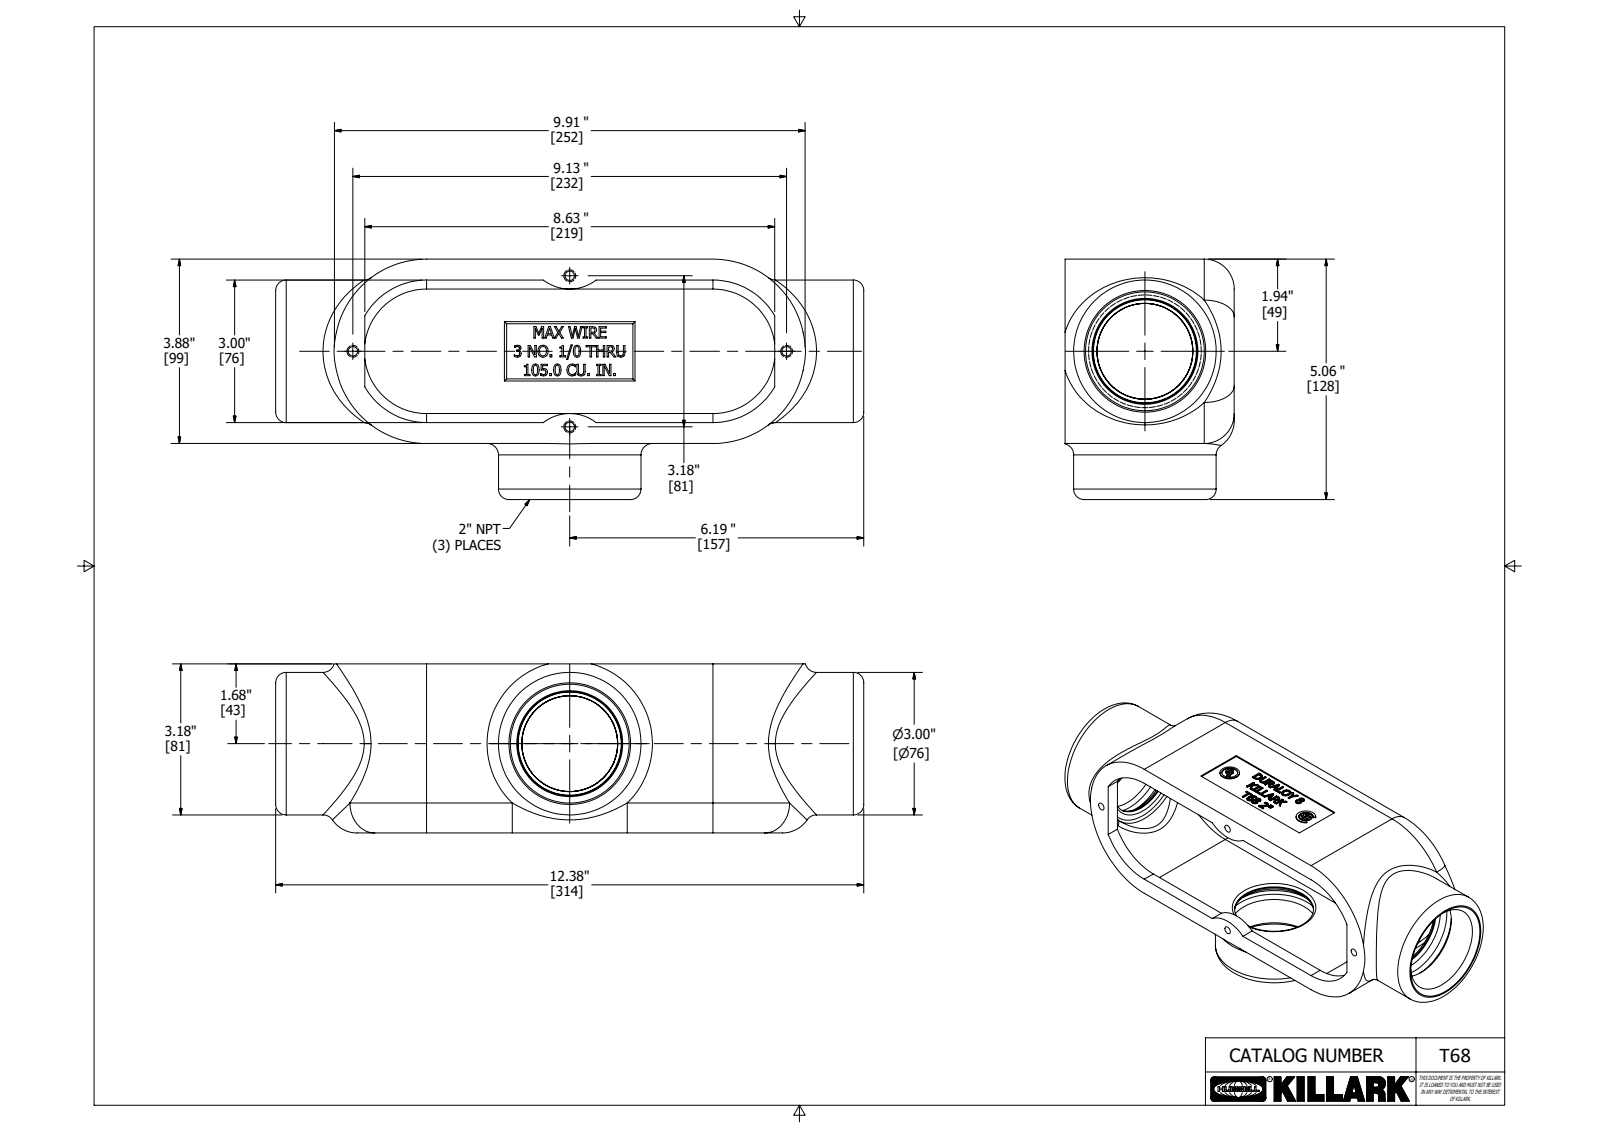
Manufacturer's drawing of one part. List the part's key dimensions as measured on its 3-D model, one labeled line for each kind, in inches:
Part name (STEP PRODUCT): 21745-2
STEP written by: Autodesk Inventor 2018 (AUTOMOTIVE_DESIGN)
Units: inches
Bodies: 1 solid, 830 faces (493 planar, 45 cylindrical, 292 other)
Overall size (bounding box): 12.381 × 5.059 × 3.62
Volume: 35.54 in³ · Surface area: 282.9 in²
Round holes (diameter × count): ⌀0.196 ×4, ⌀2.381 ×2, ⌀0.407 ×1
Round bosses / shafts (diameter × count): ⌀3 ×2, ⌀0.5 ×1
Partial cylindrical surfaces — rounded edges, fillets, slot ends (radius × count): R0.41 ×2, R0.63 ×2, R0.906 ×2, R1.5 ×2, R1.72 ×2, R1.94 ×2, R0.016 ×1, R0.063 ×1
Main face-to-face distances: 0.22, 3.66, 3.44, 3.56, 3.34, 3.88, 3.23, 3.01, 0.33, 3.85
Hole centre spacings: 4.834, 1.395, 3.18, 9.13
